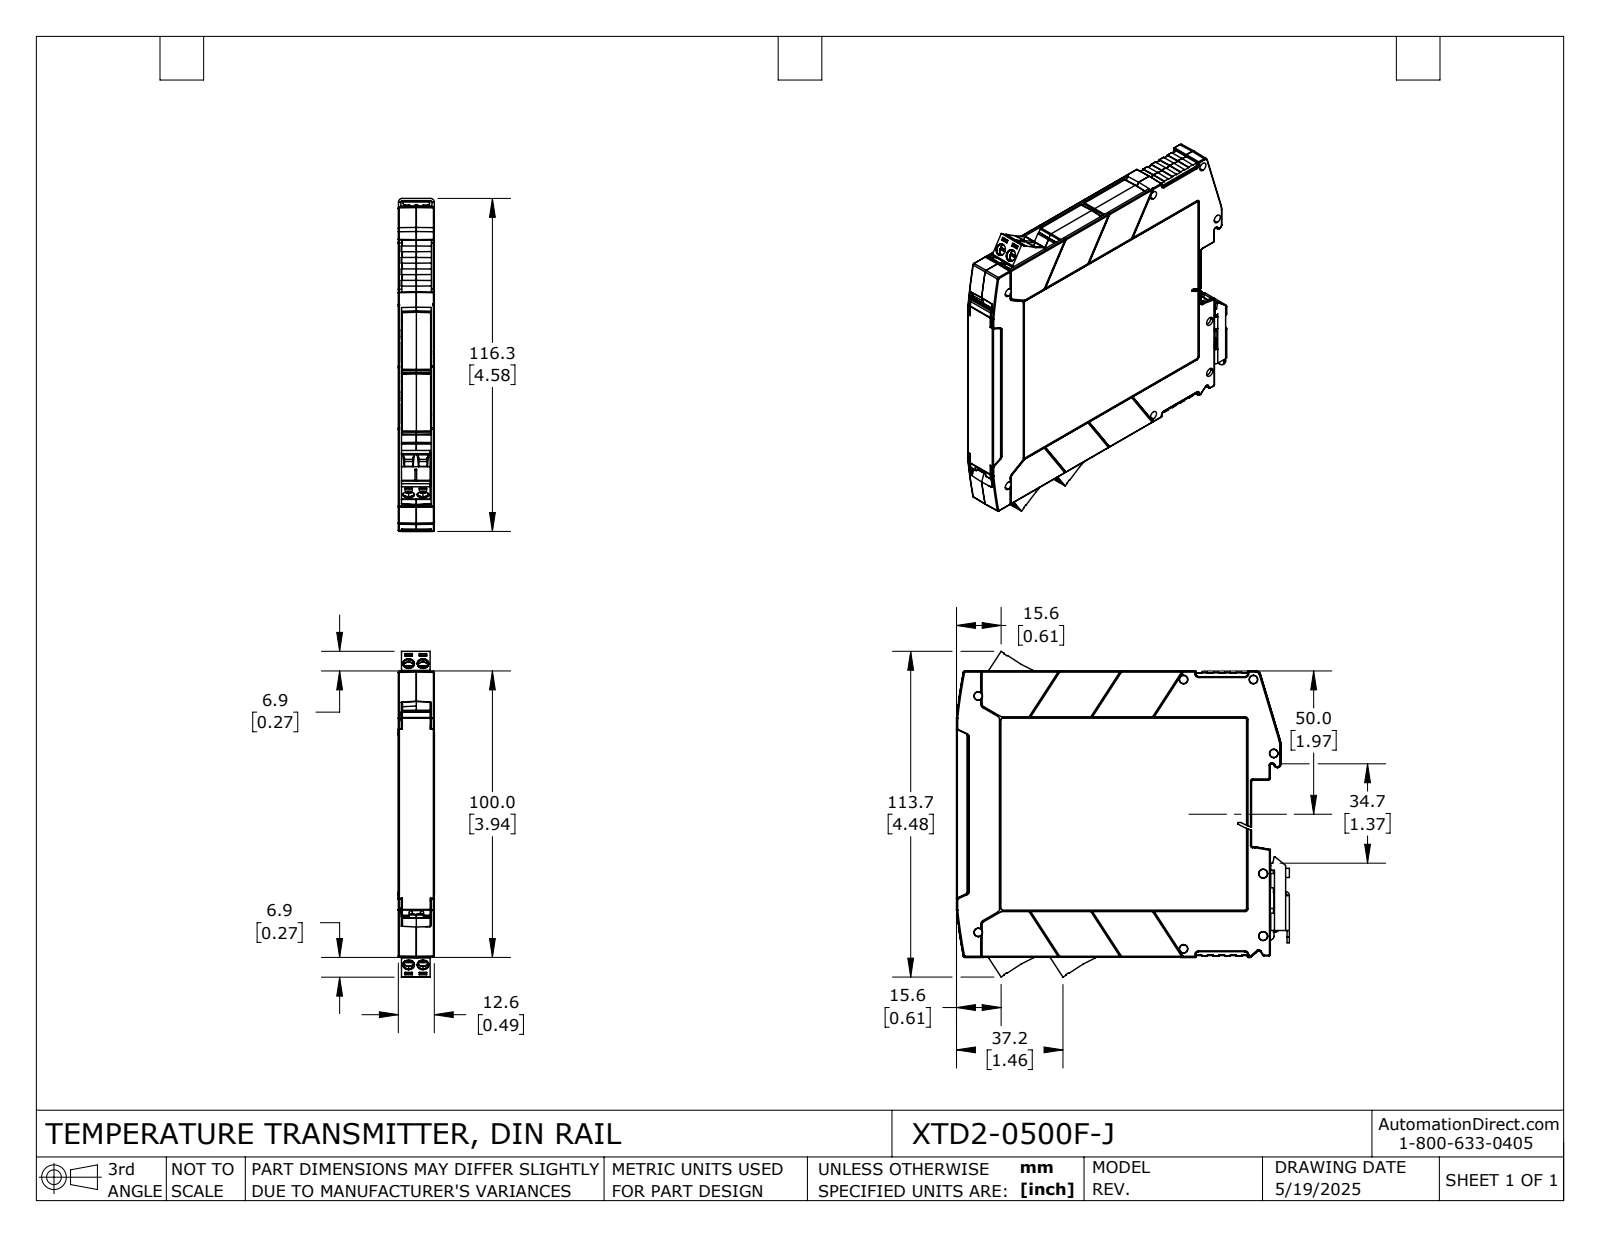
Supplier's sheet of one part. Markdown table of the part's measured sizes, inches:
| quantity | value |
| --- | --- |
| part name | XTD2-0500F-J |
| STEP written by | SolidWorks 2024 (AUTOMOTIVE_DESIGN) |
| units | inches |
| bodies | 14 solids, 3337 faces (1910 planar, 596 cylindrical, 831 other) |
| overall size | 4.577 × 4.478 × 0.496 |
| volume | 2.41 in³ |
| surface area | 101.5 in² |
| round holes (diameter × count) | 0.063 × 6, 0.11 × 6, 0.152 × 6, 0.159 × 6 |
| round bosses / shafts (diameter × count) | 0.156 × 6, 0.098 × 6, 0.059 × 2, 0.053 × 2 |
| partial cylindrical surfaces (radius × count) | 0.008 × 89, 0.012 × 78, 0.02 × 71, 0.039 × 22, 0.004 × 20, 0.016 × 13, 0.006 × 12, 0.028 × 8 |
| main face-to-face distances | 0.049, 0.445, 0.494, 0.396, 0.043, 0.451, 0.402, 0.031, 0.198, 0.247 |
| hole center spacings | 0.197, 0.464, 0.504, 0.713, 0.739 |
